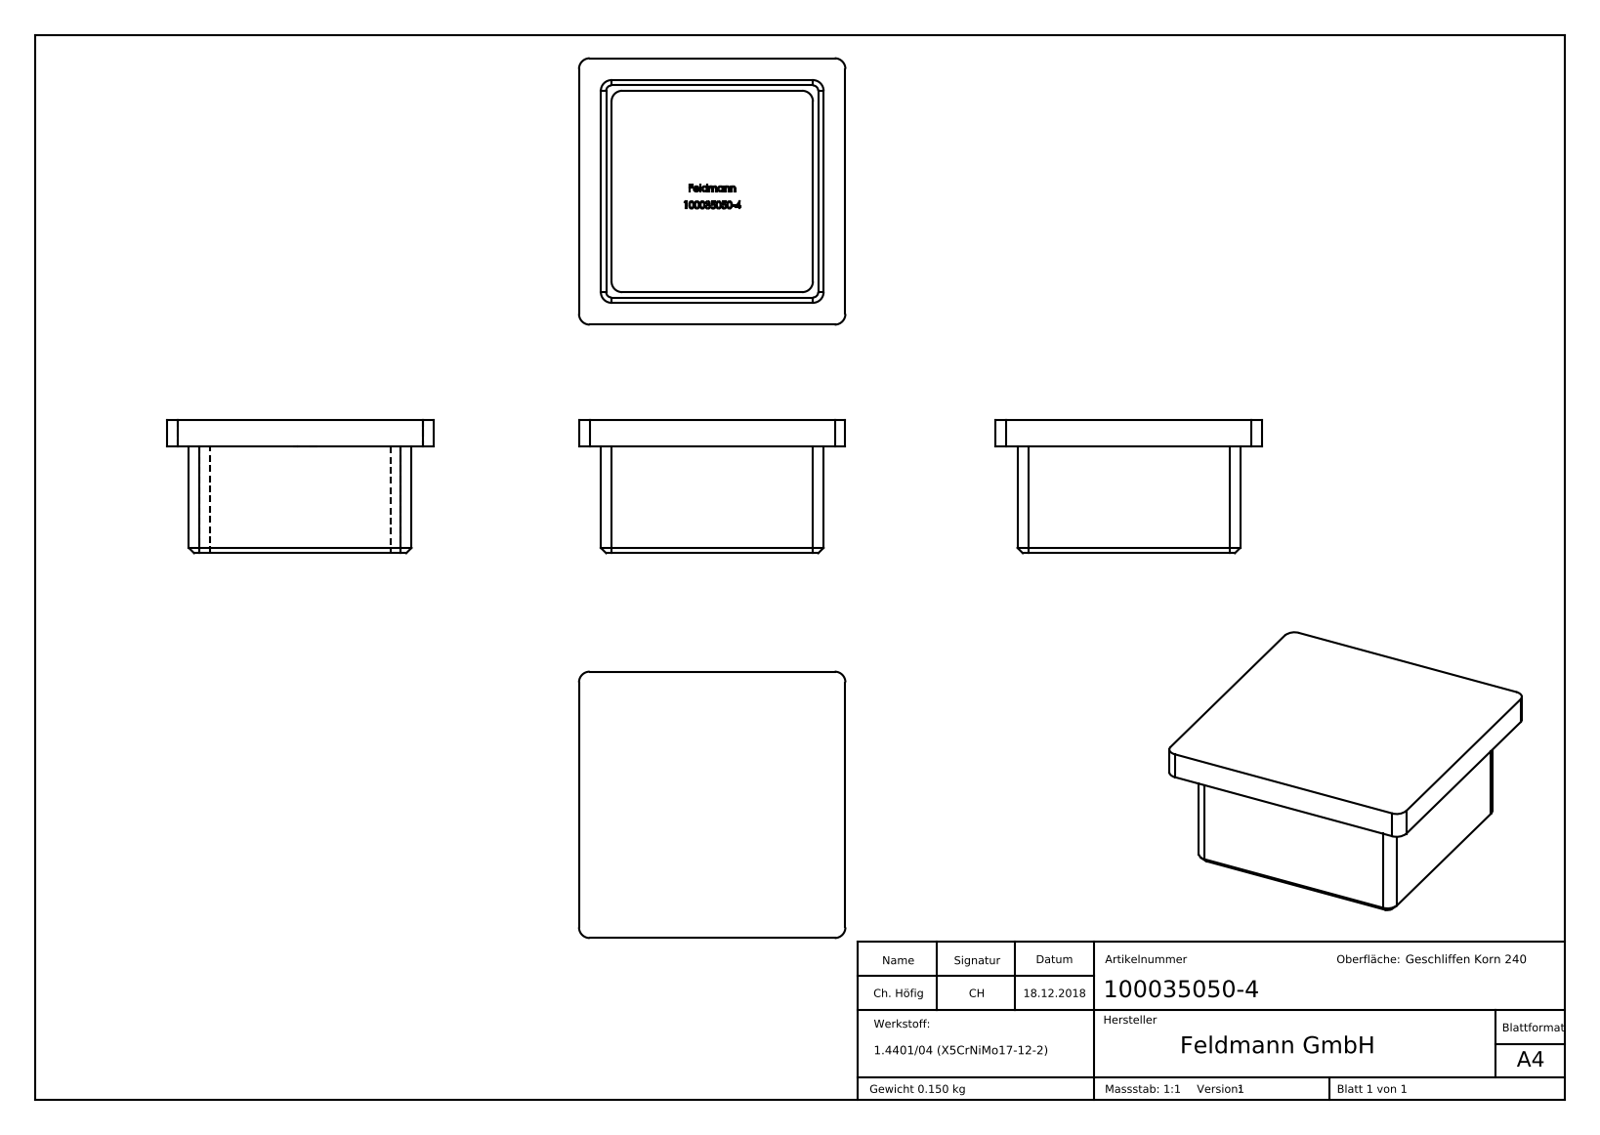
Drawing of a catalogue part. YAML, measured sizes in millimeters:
part_name: "100035050-4"
step_written_by: "SolidWorks 2015 (CONFIG_CONTROL_DESIGN)"
units: millimeters
bodies: {solids: 1, faces: 279, planar: 140, cylindrical: 12, other: 127}
overall_size: [50, 50, 25]
volume: 18769
surface_area: 12120
partial_cylinders:
  - {radius: 2, count: 12}
face_to_face_distances: [2, 39.8, 5, 41.8, 37.8, 4.1, 6.1, 43.9, 45.9, 50]
